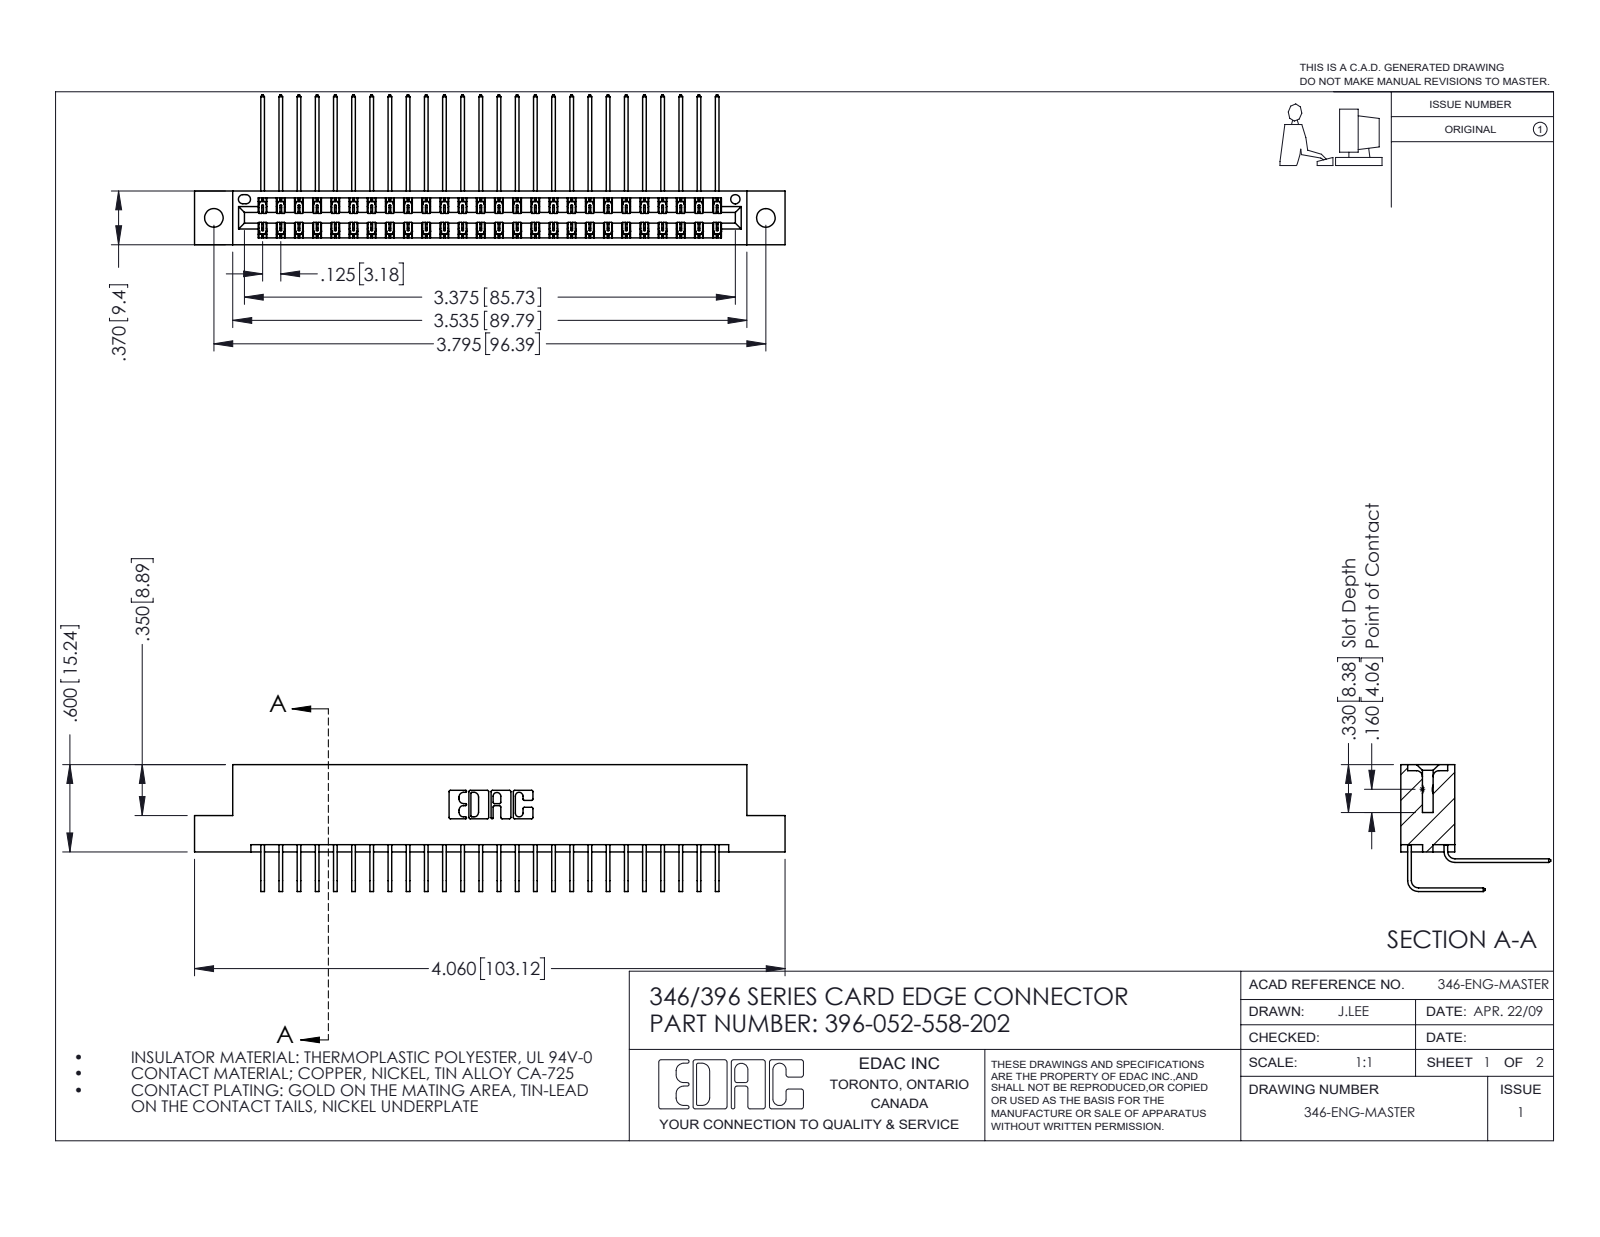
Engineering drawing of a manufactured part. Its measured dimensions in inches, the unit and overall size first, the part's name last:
Units: inches
Overall size (bounding box): 4.06 × 1.03 × 0.873
Round holes (diameter × count): ⌀0.128 ×2, ⌀0.064 ×1
Partial cylindrical surfaces — rounded edges, fillets, slot ends (radius × count): R0.006 ×78, R0.01 ×22, R0.007 ×6, R0.031 ×6, R0.026 ×3, R0.014 ×2, R0.022 ×2, R0.024 ×2
Main face-to-face distances: 0.322, 0.048, 0.25, 0.025, 0.37, 0.298, 0.072, 0.275, 0.148, 0.222
Hole centre spacings: 0.246, 3.587, 3.795
Volume: 0.622 in³ · Surface area: 23.14 in²
Bodies: 53 solids, 2930 faces (2000 planar, 930 cylindrical, 0 other)
Part name (STEP PRODUCT): 396-052-558-202; 345-292-001_558 Tail - 2; 345-292-001_558 559 Tail - 1; 346 Part_Flush Mounting Lugs - 0.128 Dia
STEP written by: SolidWorks 2016 (CONFIG_CONTROL_DESIGN)
